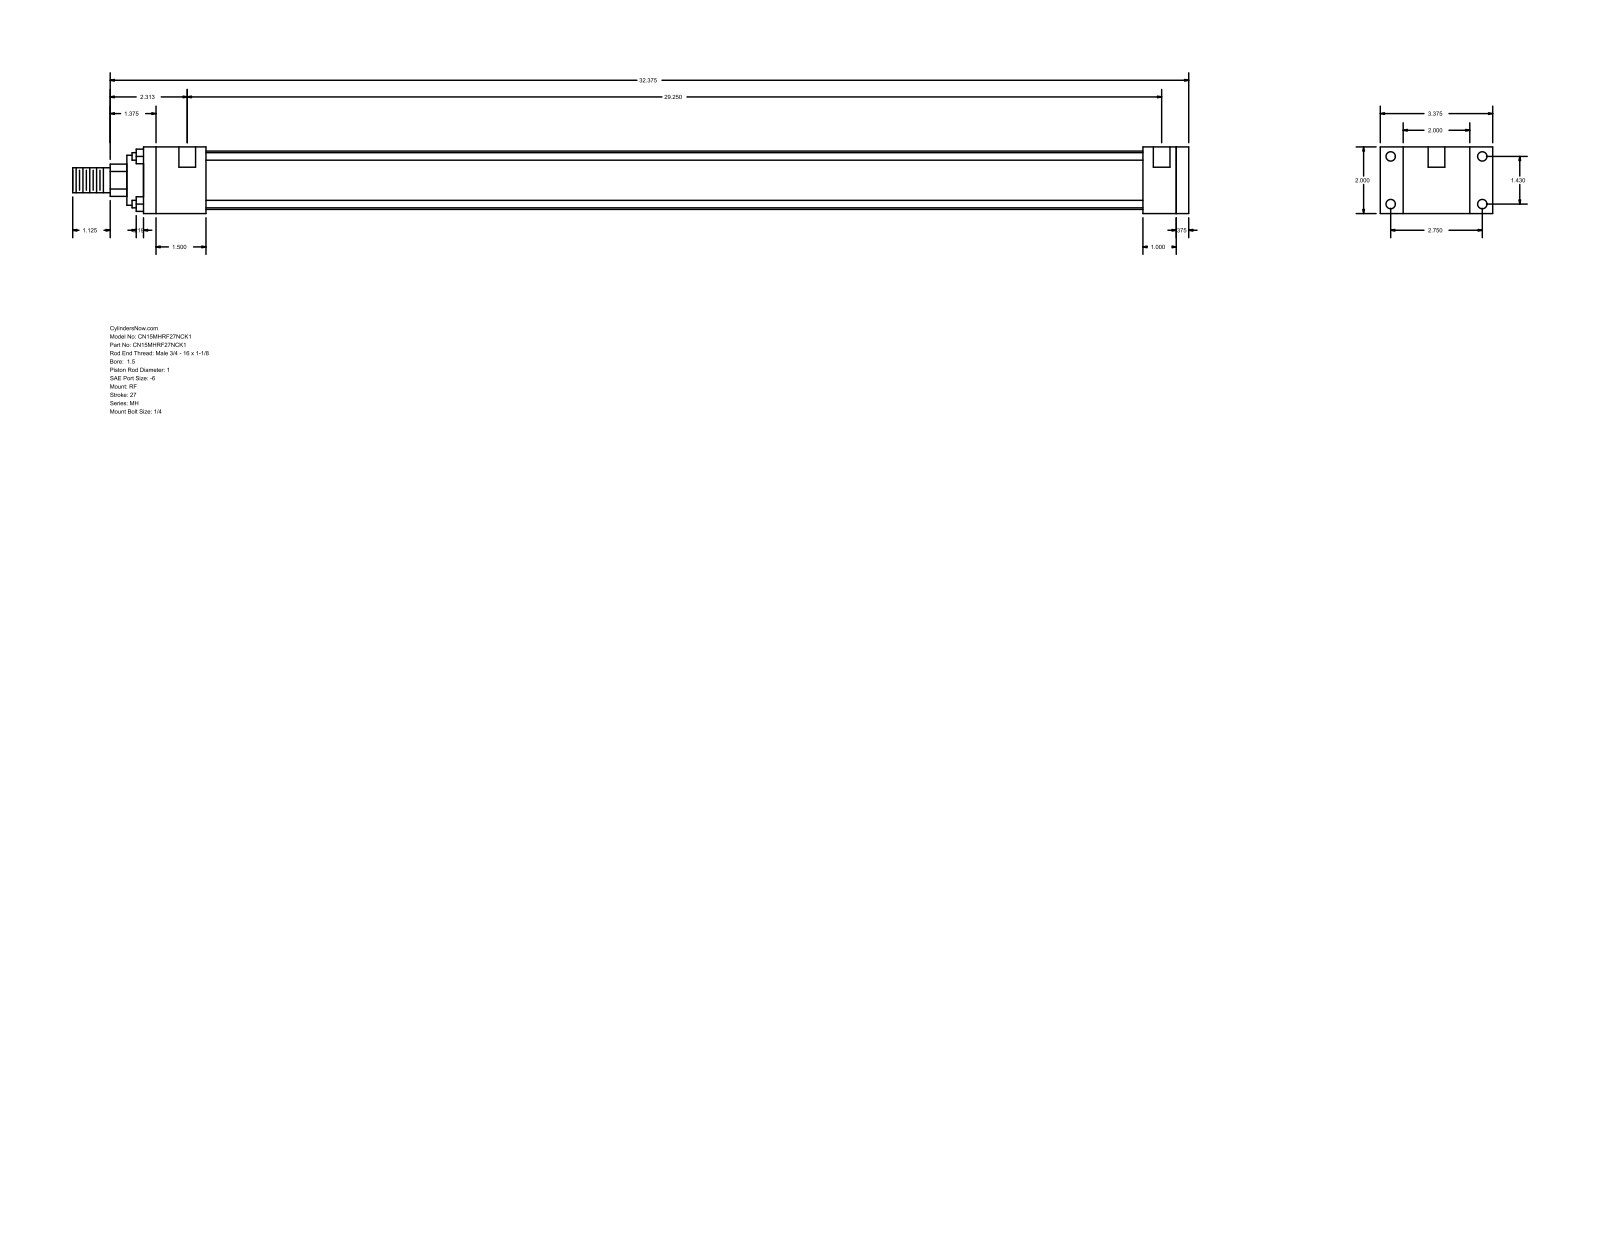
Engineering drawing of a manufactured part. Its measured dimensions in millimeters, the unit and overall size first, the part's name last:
Units: millimetres
Overall size (bounding box): 850.9 × 85.72 × 50.8
Round holes (diameter × count): ⌀5.56 ×4, ⌀7.14 ×4, ⌀12.7 ×2
Round bosses / shafts (diameter × count): ⌀5.71 ×4, ⌀44.45 ×1, ⌀38.1 ×1, ⌀25.4 ×1, ⌀19.05 ×1
Partial cylindrical surfaces — rounded edges, fillets, slot ends (radius × count): R12.29 ×1
Main face-to-face distances: 50.8, 9.53, 787.4, 25.4, 796.93, 17.46, 68.26, 762, 34.93, 47.63
Hole centre spacings: 36.32, 69.84, 78.72, 746.13, 3.18, 742.95
Bodies: 0 solids, 92 faces (64 planar, 28 cylindrical, 0 other)
Part name (STEP PRODUCT): MH_RF__0150_1
STEP written by: GSSL Pune (CONFIG_CONTROL_DESIGN)
